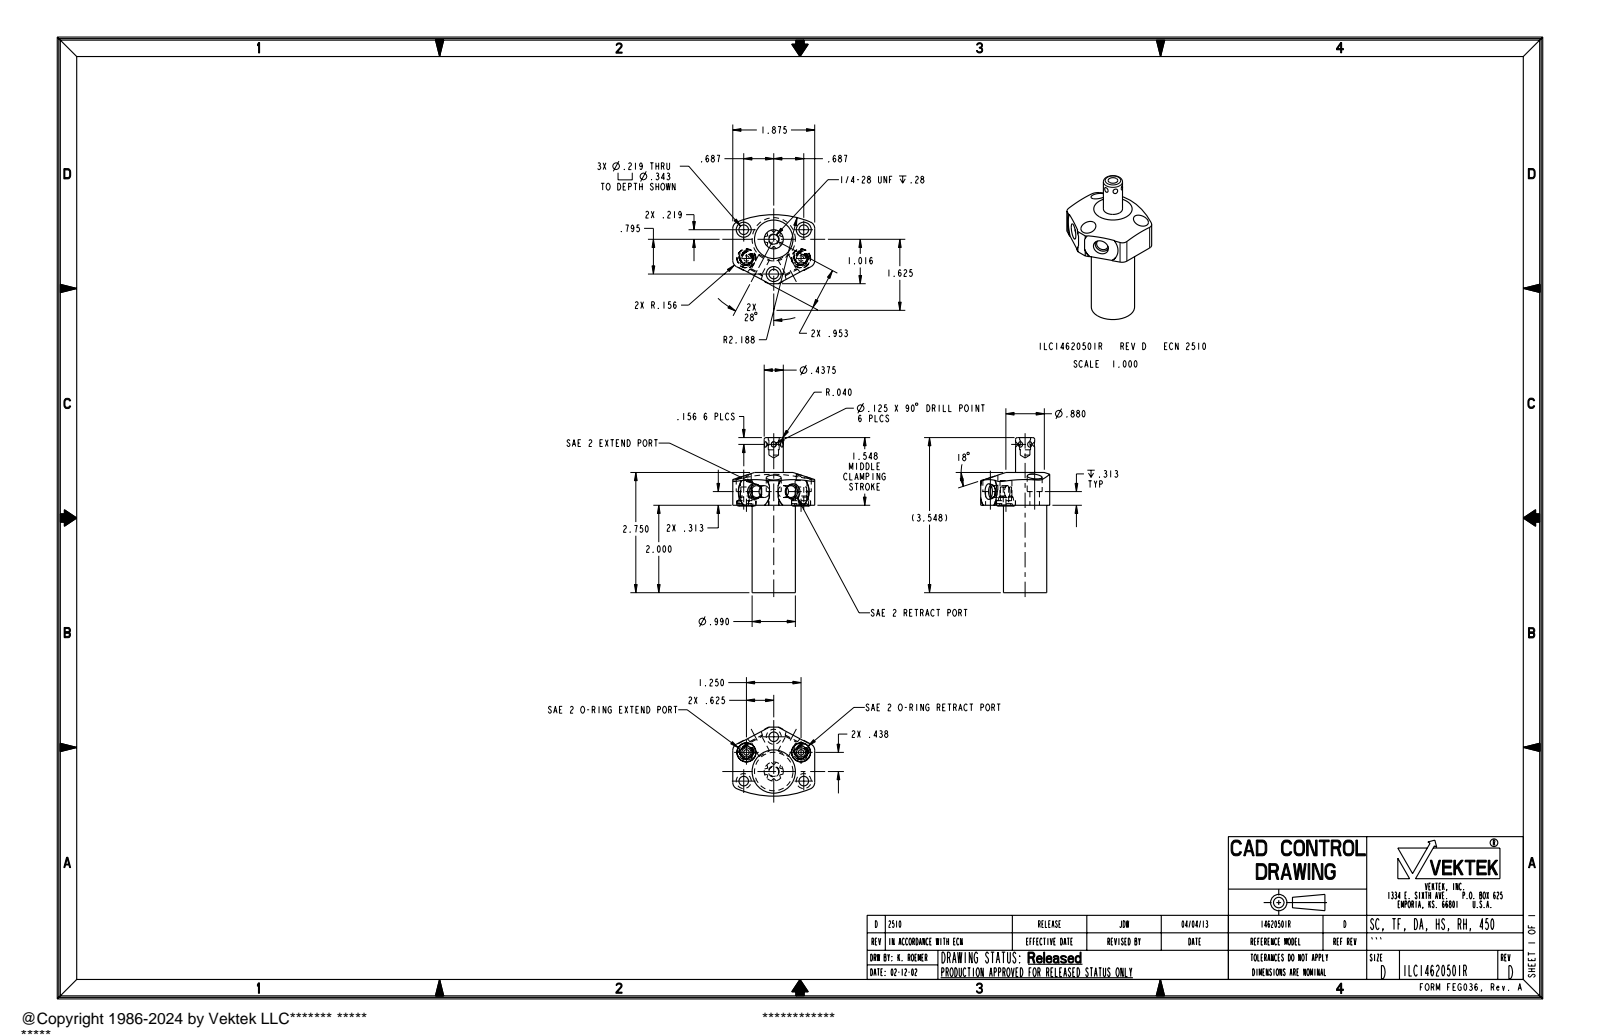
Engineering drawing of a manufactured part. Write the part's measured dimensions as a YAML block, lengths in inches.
part_name: "ILC14620501R"
step_written_by: "PRO/ENGINEER BY PARAMETRIC TECHNOLOGY CORPORATION, 2007460 (AUTOMOTIVE_DESIGN_CC2)"
units: inches
bodies: {solids: 1, faces: 136, planar: 35, cylindrical: 59, other: 42}
overall_size: [3.548, 1.875, 1.579]
volume: 3.083
surface_area: 21.3
round_holes:
  - {diameter: 0.272, count: 4}
  - {diameter: 0.219, count: 3}
  - {diameter: 0.343, count: 3}
  - {diameter: 0.125, count: 2}
  - {diameter: 0.438, count: 2}
  - {diameter: 0.221, count: 1}
round_bosses_or_shafts:
  - {diameter: 0.43, count: 2}
  - {diameter: 0.256, count: 2}
  - {diameter: 0.21, count: 2}
  - {diameter: 0.99, count: 1}
  - {diameter: 0.437, count: 1}
  - {diameter: 0.25, count: 1}
partial_cylinders:
  - {radius: 0.156, count: 4}
  - {radius: 0.412, count: 2}
  - {radius: 2.188, count: 1}
face_to_face_distances: [2, 2.75, 0.75, 1.875, 0.313, 0.105, 2.313, 0.437, 2.565, 0.565]
hole_center_spacings: [0.66, 0.72, 0.721, 0.763, 1.225, 1.468, 0.795, 1.25]
